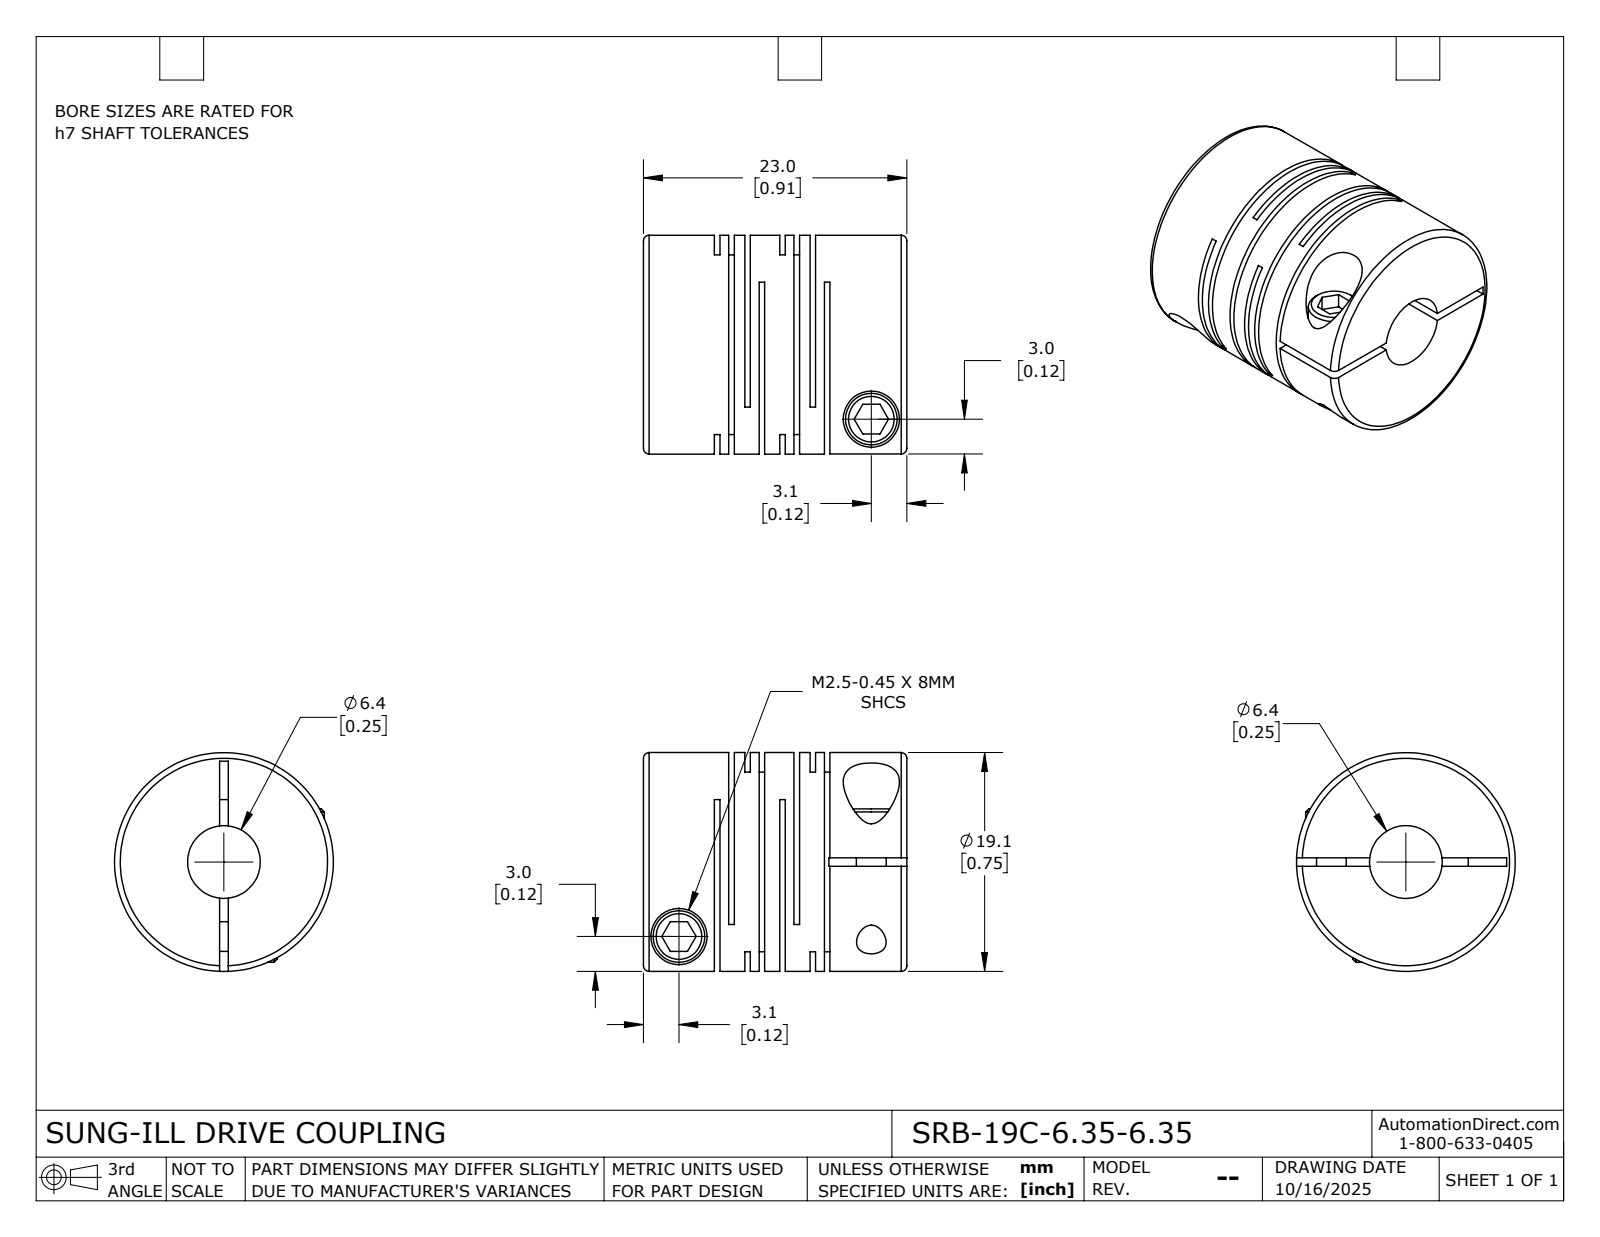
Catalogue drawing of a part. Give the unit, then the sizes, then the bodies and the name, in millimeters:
Units: millimetres
Overall size (bounding box): 23 × 19.1 × 19.1
Round holes (diameter × count): ⌀2.6 ×2, ⌀4.9 ×2, ⌀6.35 ×1
Round bosses / shafts (diameter × count): ⌀4.5 ×2, ⌀19.1 ×1
Main face-to-face distances: 2.65, 0.48, 1.25, 5.7, 2.17, 3.05, 5.22, 0.77, 4.45, 1.4
Volume: 4 816 mm³ · Surface area: 5 966 mm²
Bodies: 1 solid, 115 faces (60 planar, 42 cylindrical, 13 other)
Part name (STEP PRODUCT): SRB-19C-6.35-6.35
STEP written by: SolidWorks 2024 (CONFIG_CONTROL_DESIGN)
